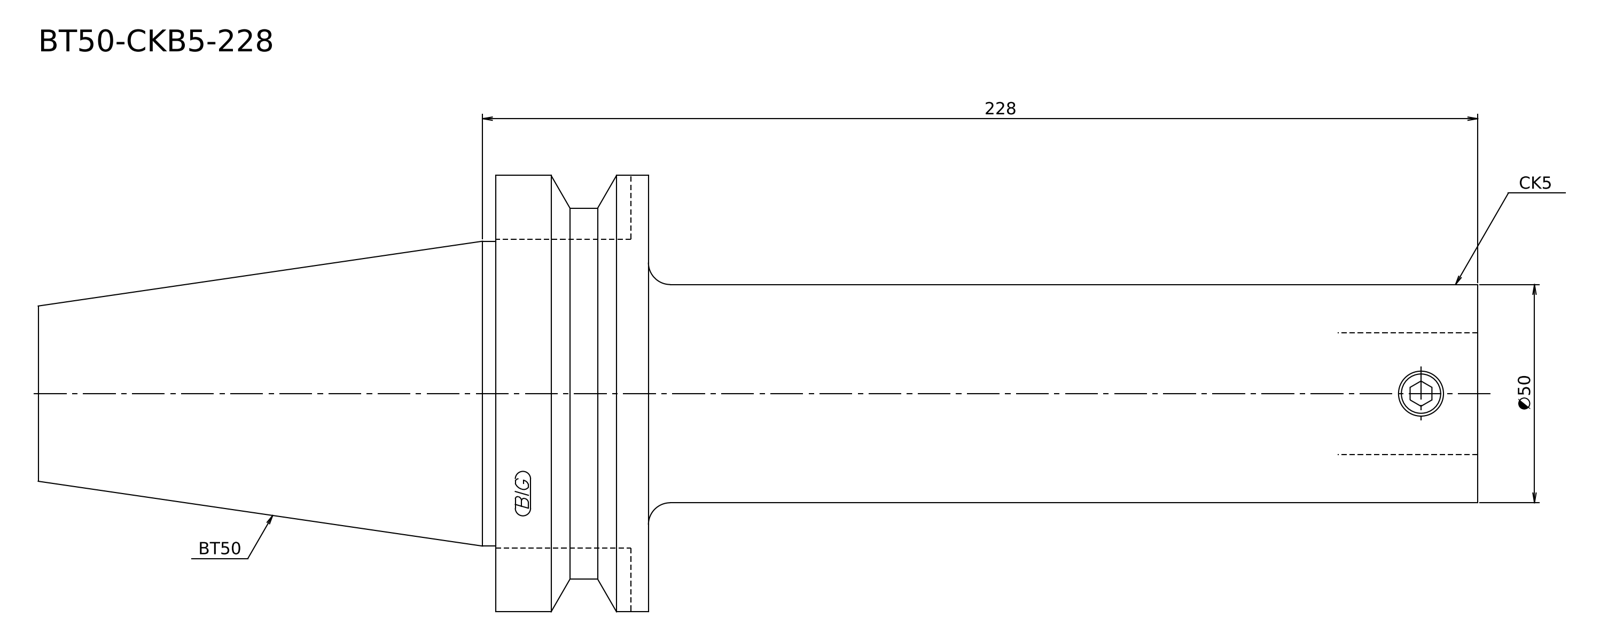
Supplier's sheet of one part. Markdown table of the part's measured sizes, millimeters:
| quantity | value |
| --- | --- |
| STEP written by | Kubotek KeyCreator V8.5.1 (14335) (CONFIG_CONTROL_DESIGN) |
| units | millimeters |
| bodies | 1 solid, 13 faces (4 planar, 5 cylindrical, 4 other) |
| overall size | 329.8 × 100 × 100 |
| volume | 885 804 mm³ |
| surface area | 74 005 mm² |
| round bosses / shafts (diameter × count) | 100 × 1, 85 × 1, 69.85 × 1, 50 × 1 |
| main face-to-face distances | 35, 190, 225, 329.8, 139.8, 104.8 |
